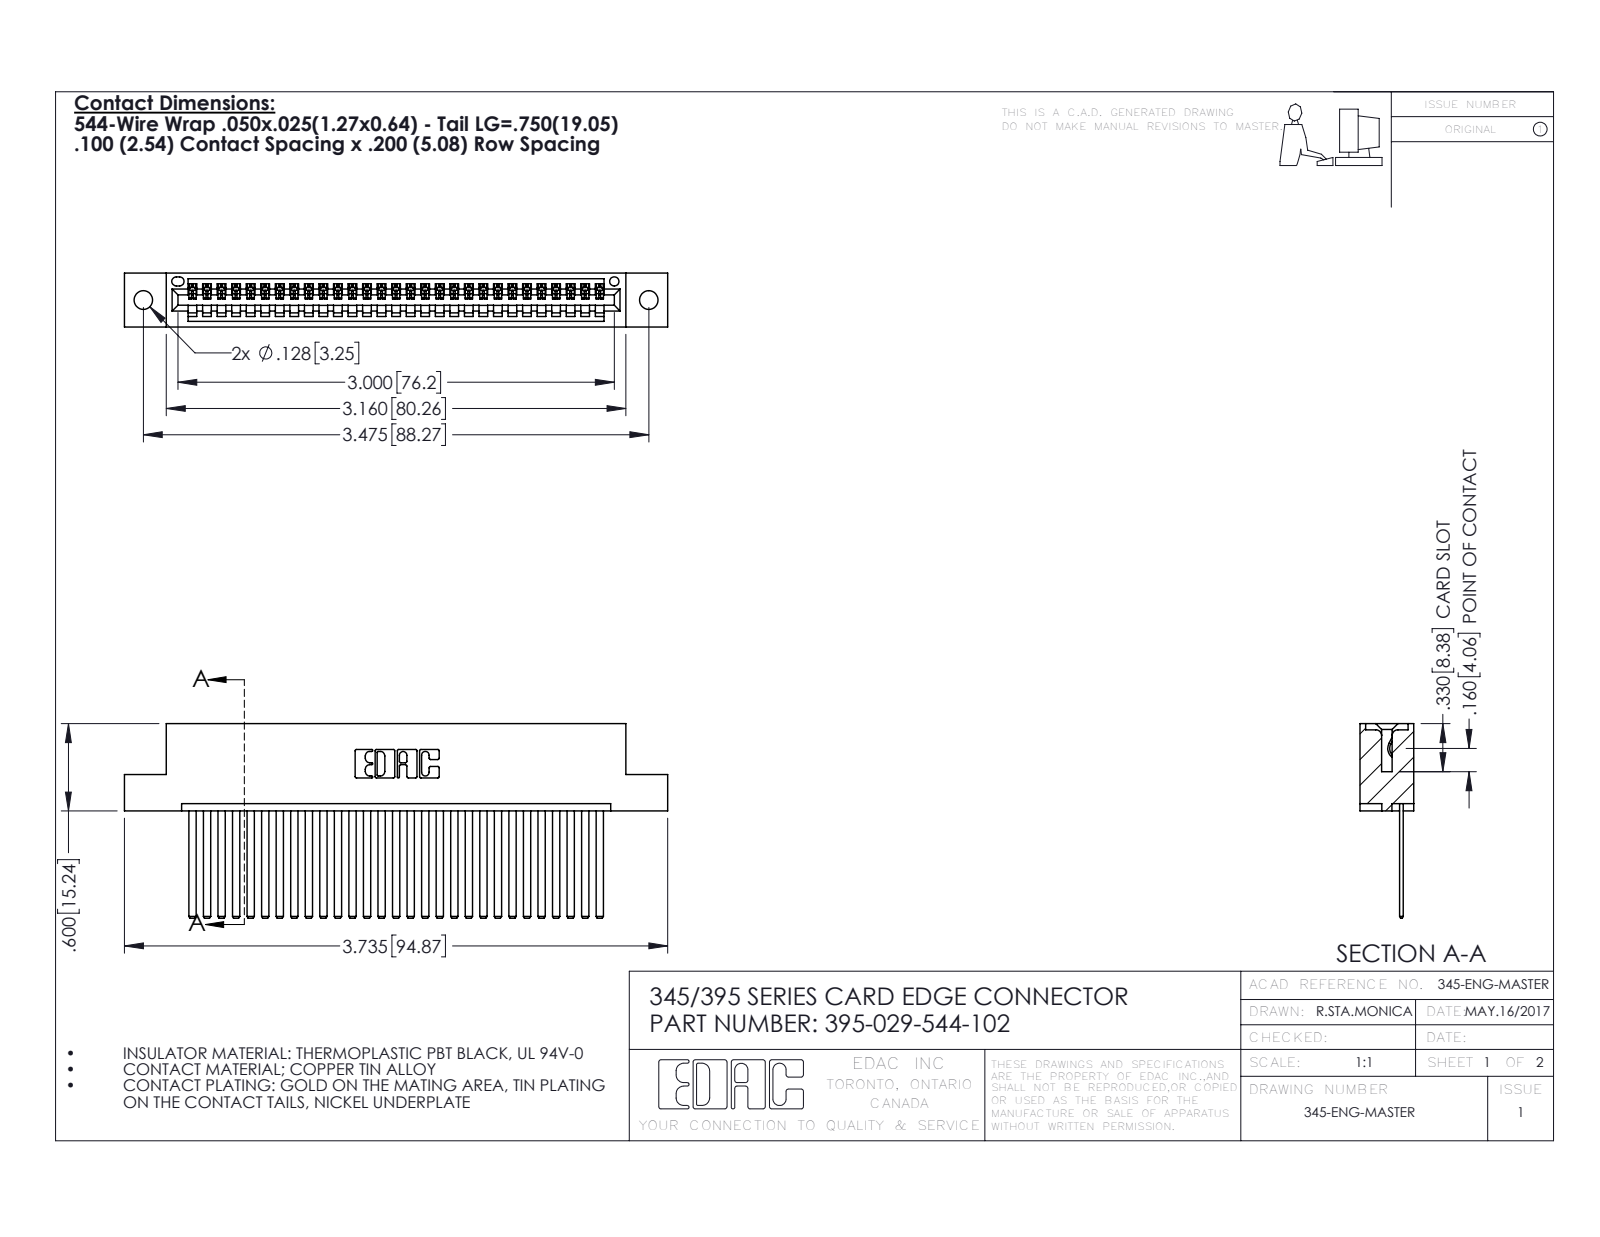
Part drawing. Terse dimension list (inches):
name: 345-292-001_345-293-144; 345 Part_Flush Mounting Lugs - 0.128 Dia; 395-029-544-102
written by: SolidWorks 2016 (CONFIG_CONTROL_DESIGN)
unit: in
bodies: 30 solids, 1634 faces (1124 planar, 510 cylindrical, 0 other)
size: 3.735 × 1.337 × 0.37
volume: 0.562 in³; area: 19.83 in²
holes: 2× ⌀0.128, 1× ⌀0.064
rounds: 58× R0.006, 22× R0.01, 6× R0.007, 6× R0.031, 3× R0.026, 2× R0.031, 2× R0.04, 1× R0.014
face distances: 0.072, 0.298, 0.098, 0.025, 0.272, 0.2, 0.37, 0.225, 0.149, 0.072
hole spacings: 0.27, 3.24, 3.475
